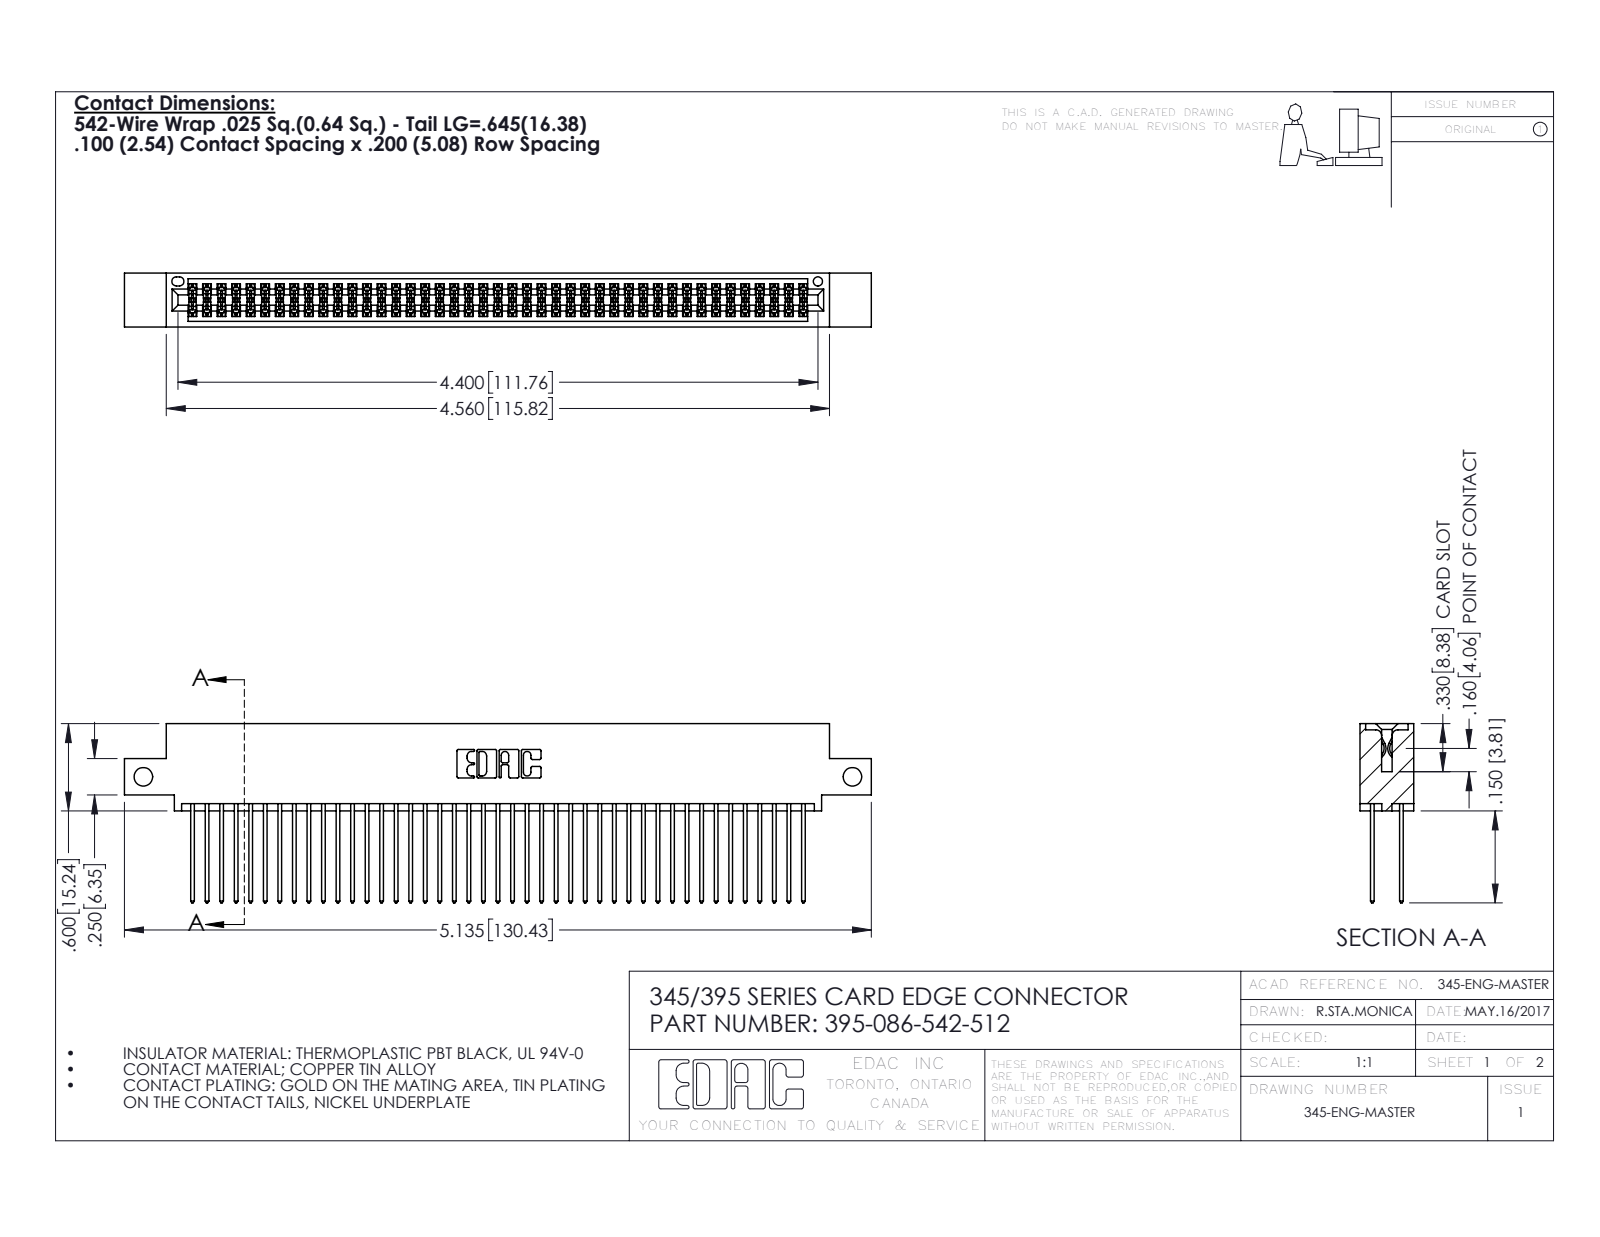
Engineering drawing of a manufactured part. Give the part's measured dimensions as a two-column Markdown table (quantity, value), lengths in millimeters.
| quantity | value |
| --- | --- |
| part name | 395-086-542-512; 345 Part_0.110 Offset - Side Mount; 345-292-001_345-293-142 |
| STEP written by | SolidWorks 2016 (CONFIG_CONTROL_DESIGN) |
| units | millimeters |
| bodies | 87 solids, 4430 faces (2922 planar, 1508 cylindrical, 0 other) |
| overall size | 130.4 × 31.3 × 9.4 |
| volume | 12 900 mm³ |
| surface area | 20 950 mm² |
| round holes (diameter × count) | 3.3 × 2, 1.6 × 1 |
| partial cylindrical surfaces (radius × count) | 0.2 × 129, 0.3 × 86, 0.3 × 22, 0.2 × 6, 0.8 × 6, 0.7 × 3, 0.4 × 2, 0.5 × 2 |
| main face-to-face distances | 7.6, 1.8, 5.1, 2.5, 6.9, 0.6, 5.7, 9.4, 4.4, 3.8 |
| hole center spacings | 123.8 |
